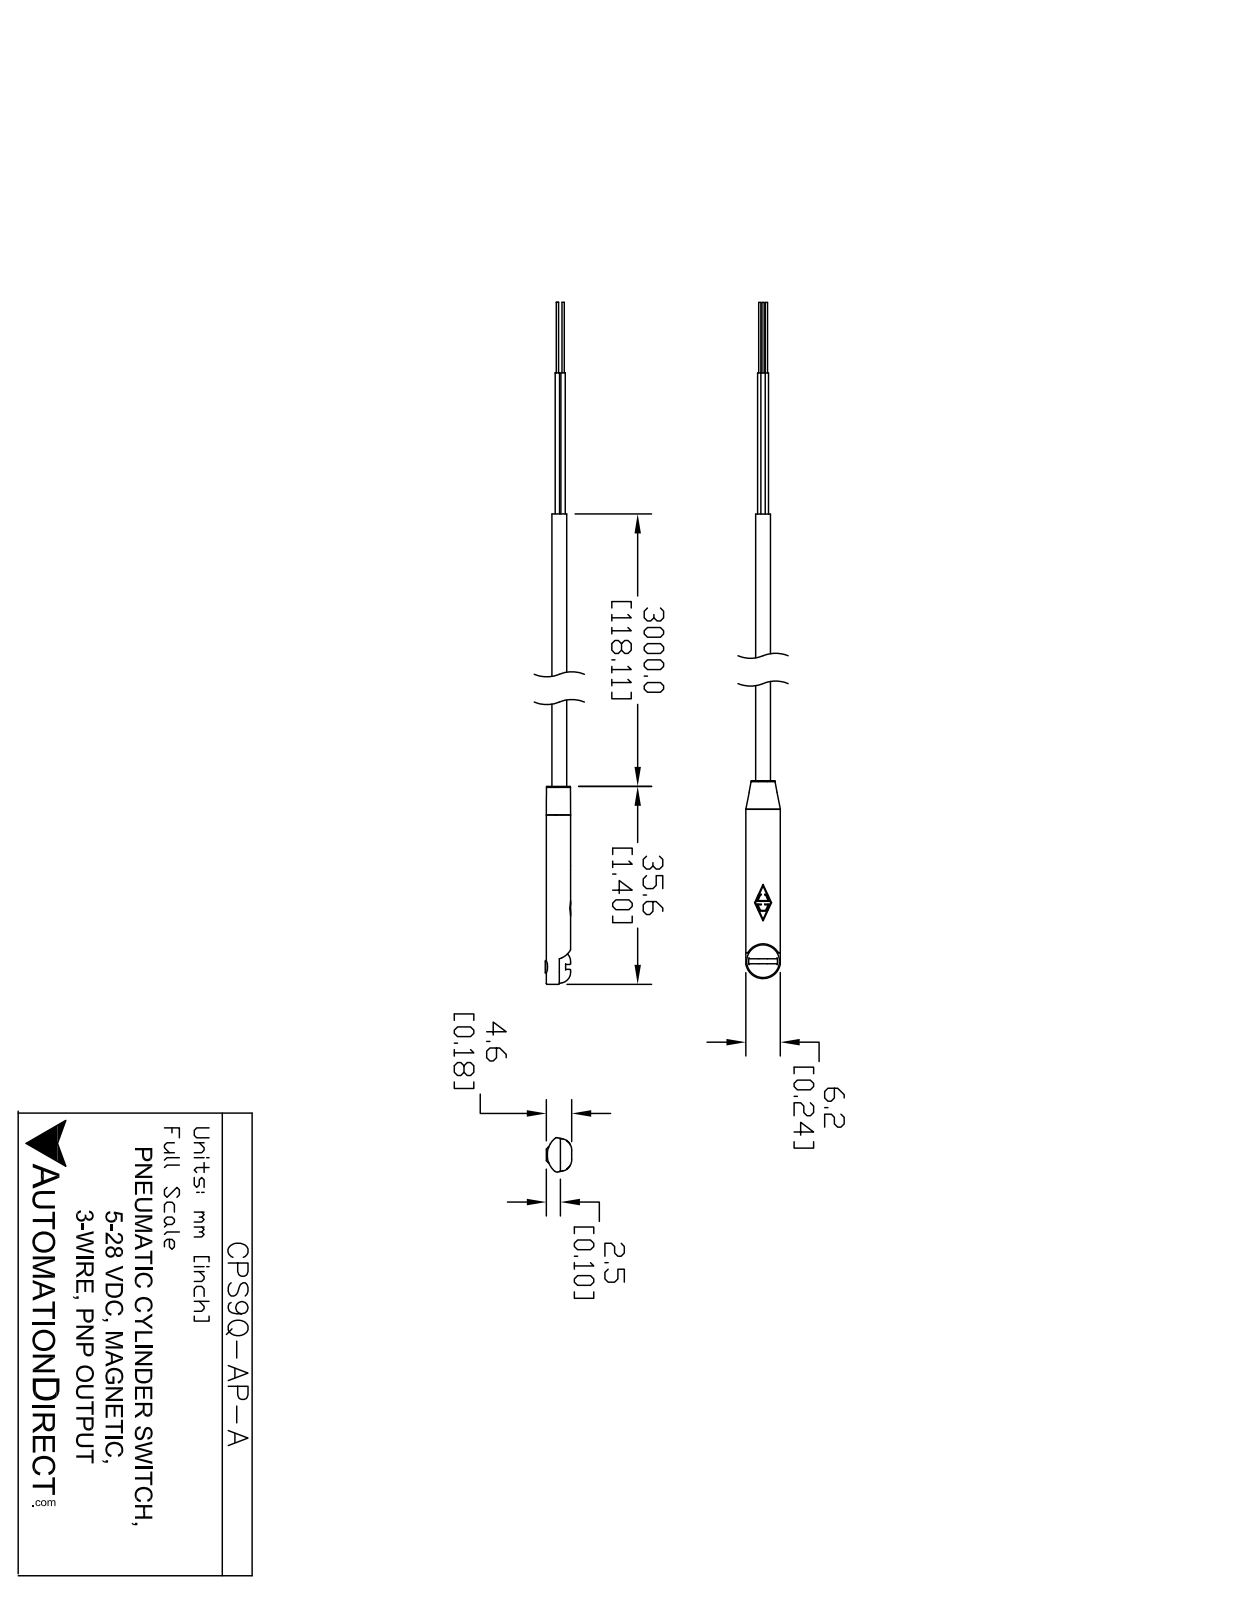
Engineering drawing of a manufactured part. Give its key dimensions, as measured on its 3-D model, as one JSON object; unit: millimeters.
{"part_name": "CPS9Q-AP-A", "step_written_by": "SolidWorks 2014 (AUTOMOTIVE_DESIGN)", "units": "millimeters", "bodies": {"solids": 3, "faces": 171, "planar": 79, "cylindrical": 50, "other": 42}, "overall_size": [182.1, 6.2, 4.6], "volume_mm3": 1400, "surface_area_mm2": 1836, "round_holes": [[0.8, 1]], "round_bosses_or_shafts": [[0.8, 3], [0.4, 3], [2.7, 1]], "partial_cylinders_radius": [[0.1, 4], [2, 3], [0.6, 2], [1.5, 2], [1.9, 2], [1.4, 1], [1.8, 1], [3.1, 1]], "face_to_face_distances": [4.4, 0.5, 3.9, 0.9, 0.4, 3.5, 1.1, 2, 1.5, 2.3]}
